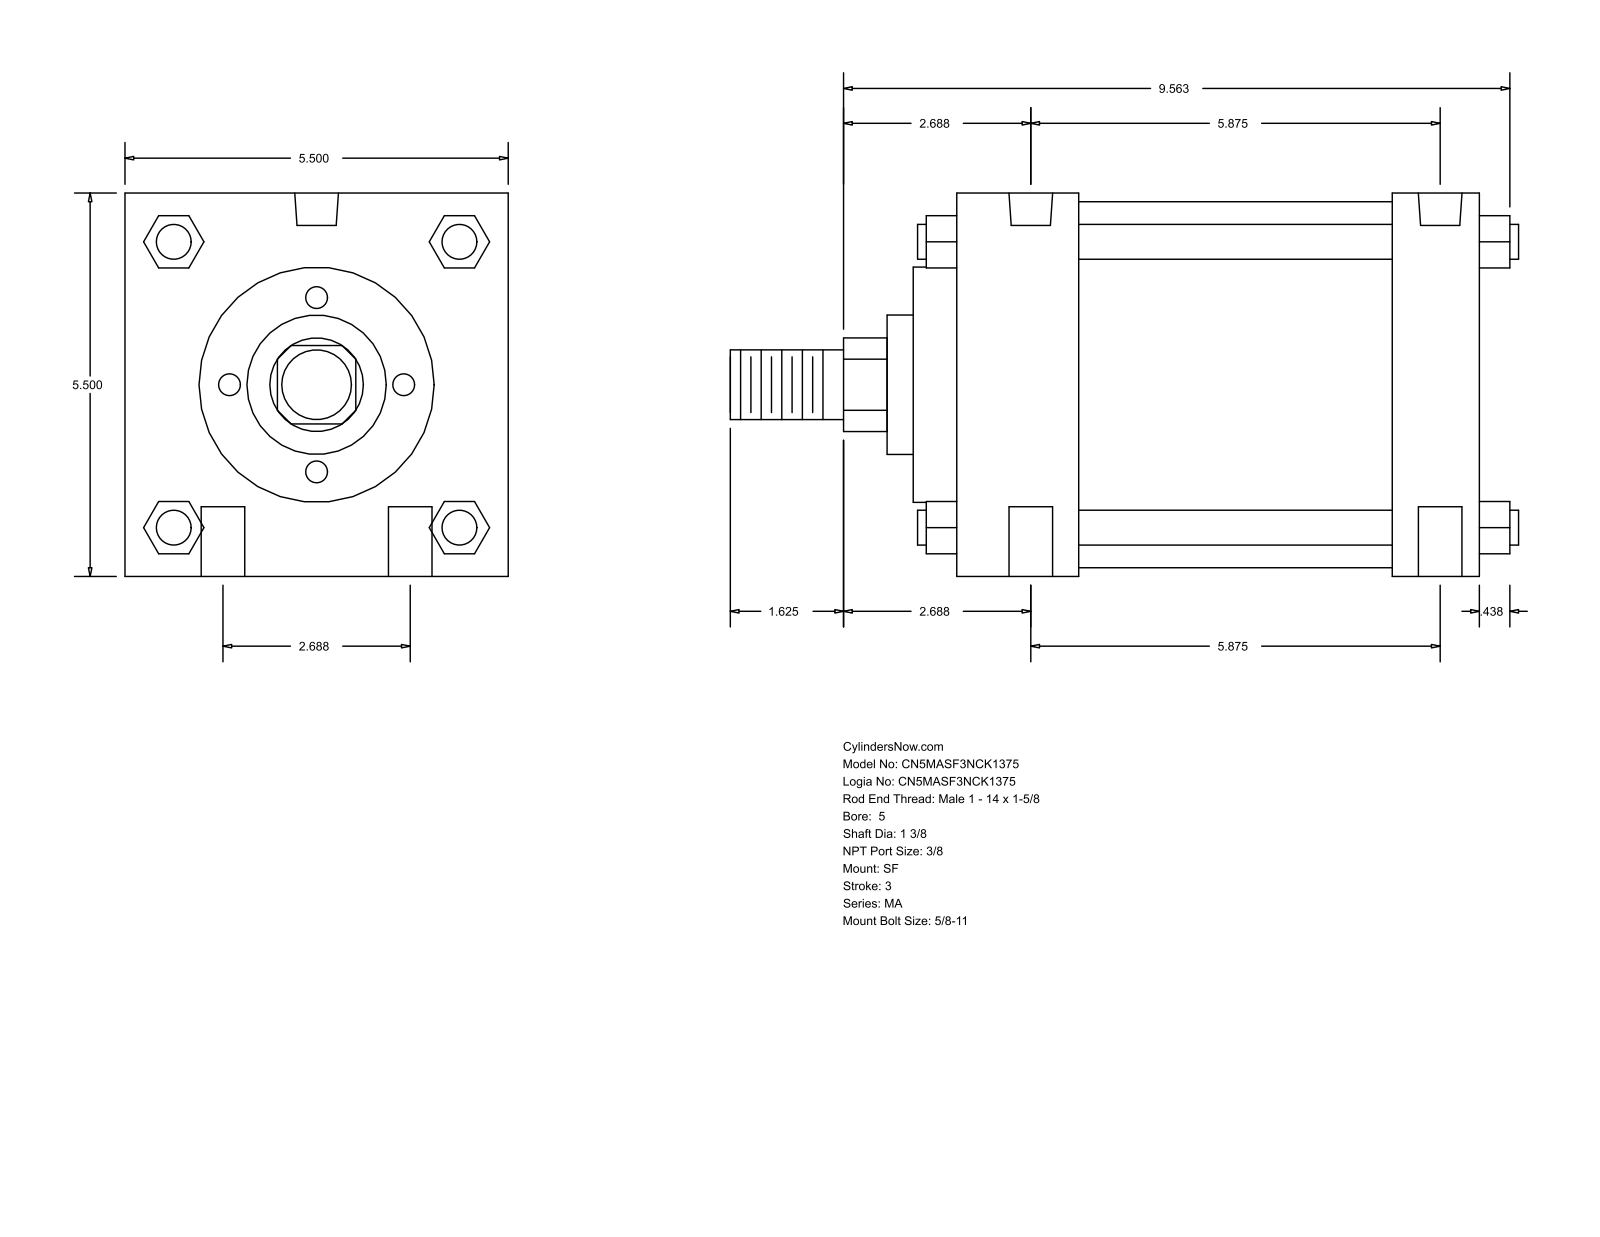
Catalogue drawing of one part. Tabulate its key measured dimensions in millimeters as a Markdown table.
| quantity | value |
| --- | --- |
| part name | MA_SF__0500_1.375 |
| STEP written by | GSSL Pune (CONFIG_CONTROL_DESIGN) |
| units | millimeters |
| bodies | 0 solids, 126 faces (95 planar, 31 cylindrical, 0 other) |
| overall size | 287.34 × 139.7 × 139.7 |
| round holes (diameter × count) | 15.88 × 4, 11.11 × 2, 15.93 × 2 |
| round bosses / shafts (diameter × count) | 12.7 × 4, 133.35 × 1, 85.72 × 1, 50.8 × 1, 34.92 × 1, 25.4 × 1 |
| partial cylindrical surfaces (radius × count) | 17.06 × 1 |
| main face-to-face distances | 139.7, 190.51, 44.45, 158.76, 114.31, 146.06, 31.75, 15.87, 60.32, 174.63 |
| hole center spacings | 34.13, 153.08, 149.23, 68.26, 164.1, 139.69 |
